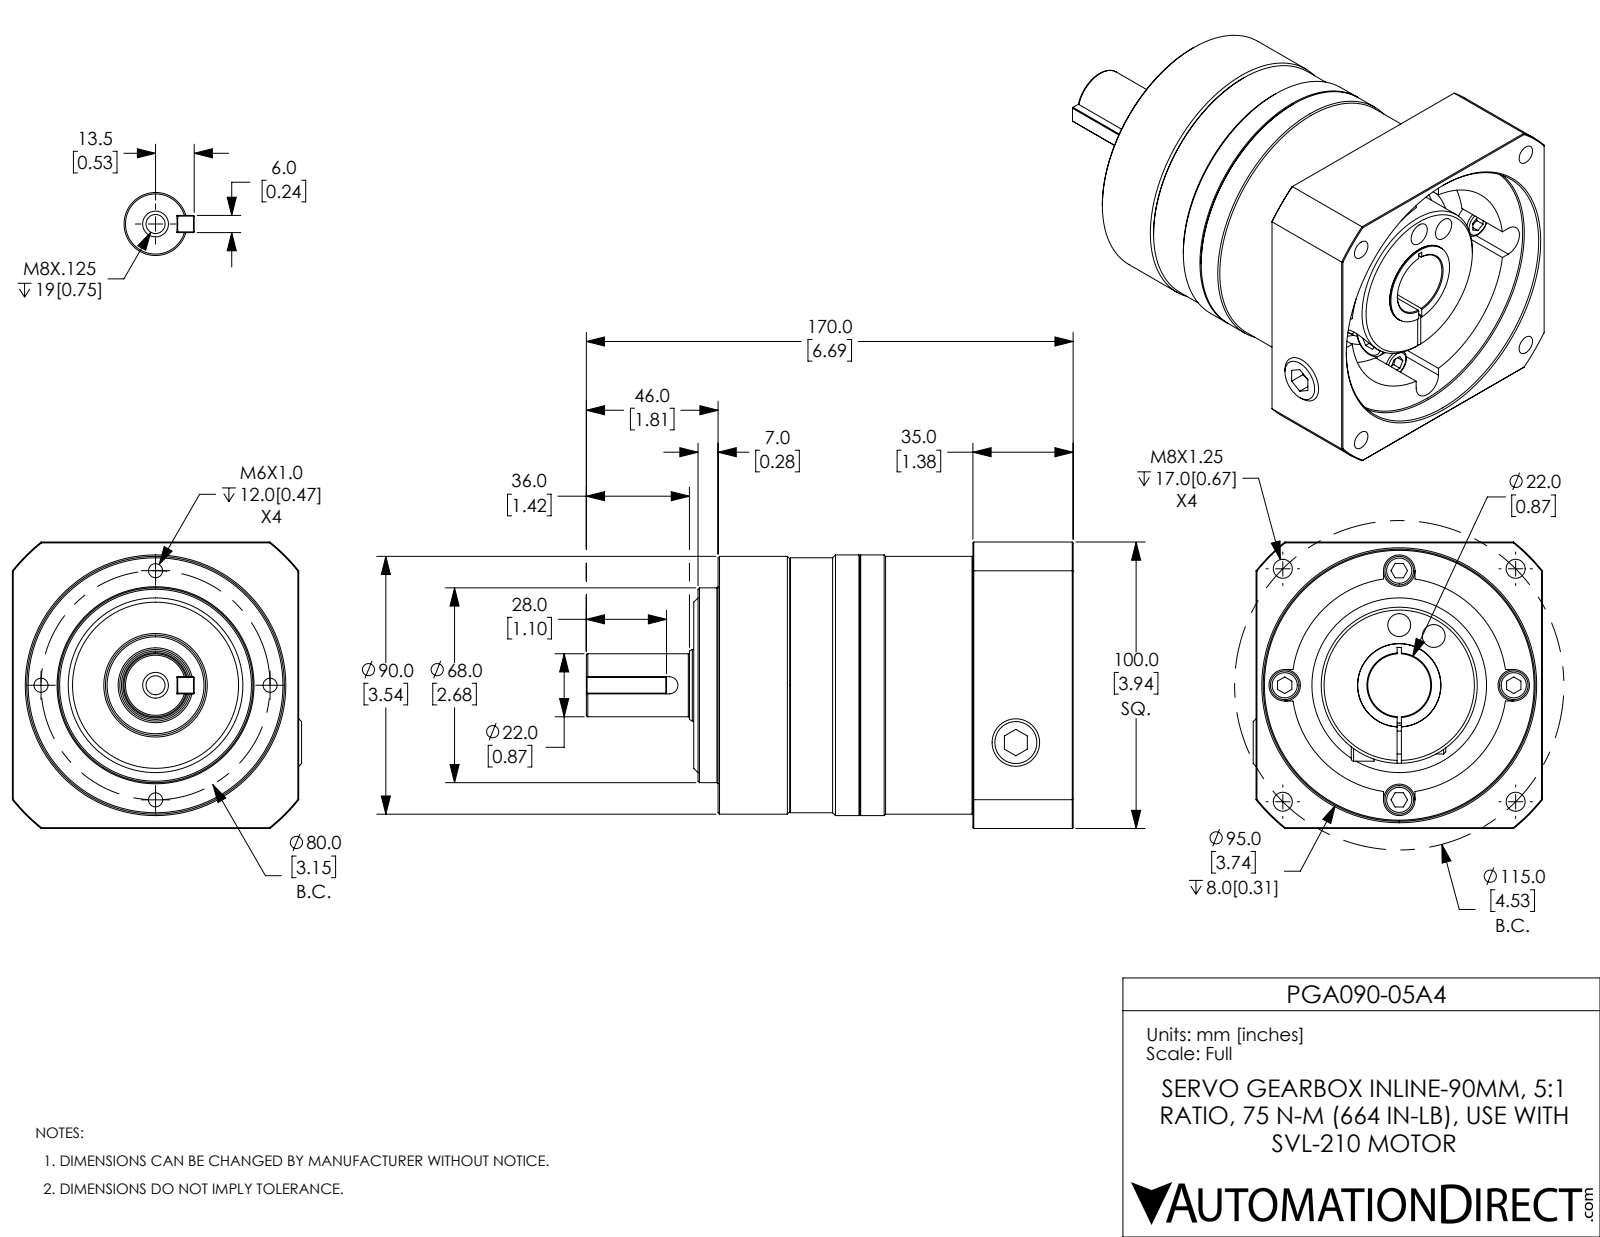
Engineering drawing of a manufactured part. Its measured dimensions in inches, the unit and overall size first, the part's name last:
Units: inches
Overall size (bounding box): 6.693 × 3.976 × 3.937
Round holes (diameter × count): ⌀0.262 ×5, ⌀0.194 ×4, ⌀0.433 ×4, ⌀0.315 ×2, ⌀0.346 ×1, ⌀0.561 ×1, ⌀0.866 ×1, ⌀2.402 ×1, ⌀2.953 ×1, ⌀3.74 ×1
Round bosses / shafts (diameter × count): ⌀0.394 ×4, ⌀3.583 ×1, ⌀3.543 ×1, ⌀3.504 ×1, ⌀2.677 ×1, ⌀2.146 ×1, ⌀1.142 ×1, ⌀1.102 ×1
Partial cylindrical surfaces — rounded edges, fillets, slot ends (radius × count): R0.118 ×1, R0.131 ×1, R0.276 ×1, R2.52 ×1
Main face-to-face distances: 3.937, 0.276, 3.78, 3.504, 0.315, 1.378, 1.102, 4.882, 1.063, 0.787
Hole centre spacings: 1.601, 3.556, 1.575, 2.227, 2.264, 3.202, 0.827, 1.778
Volume: 48.84 in³ · Surface area: 139.2 in²
Bodies: 1 solid, 328 faces (127 planar, 91 cylindrical, 110 other)
Part name (STEP PRODUCT): PGA090-05A4
STEP written by: SolidWorks 2019 (CONFIG_CONTROL_DESIGN)
